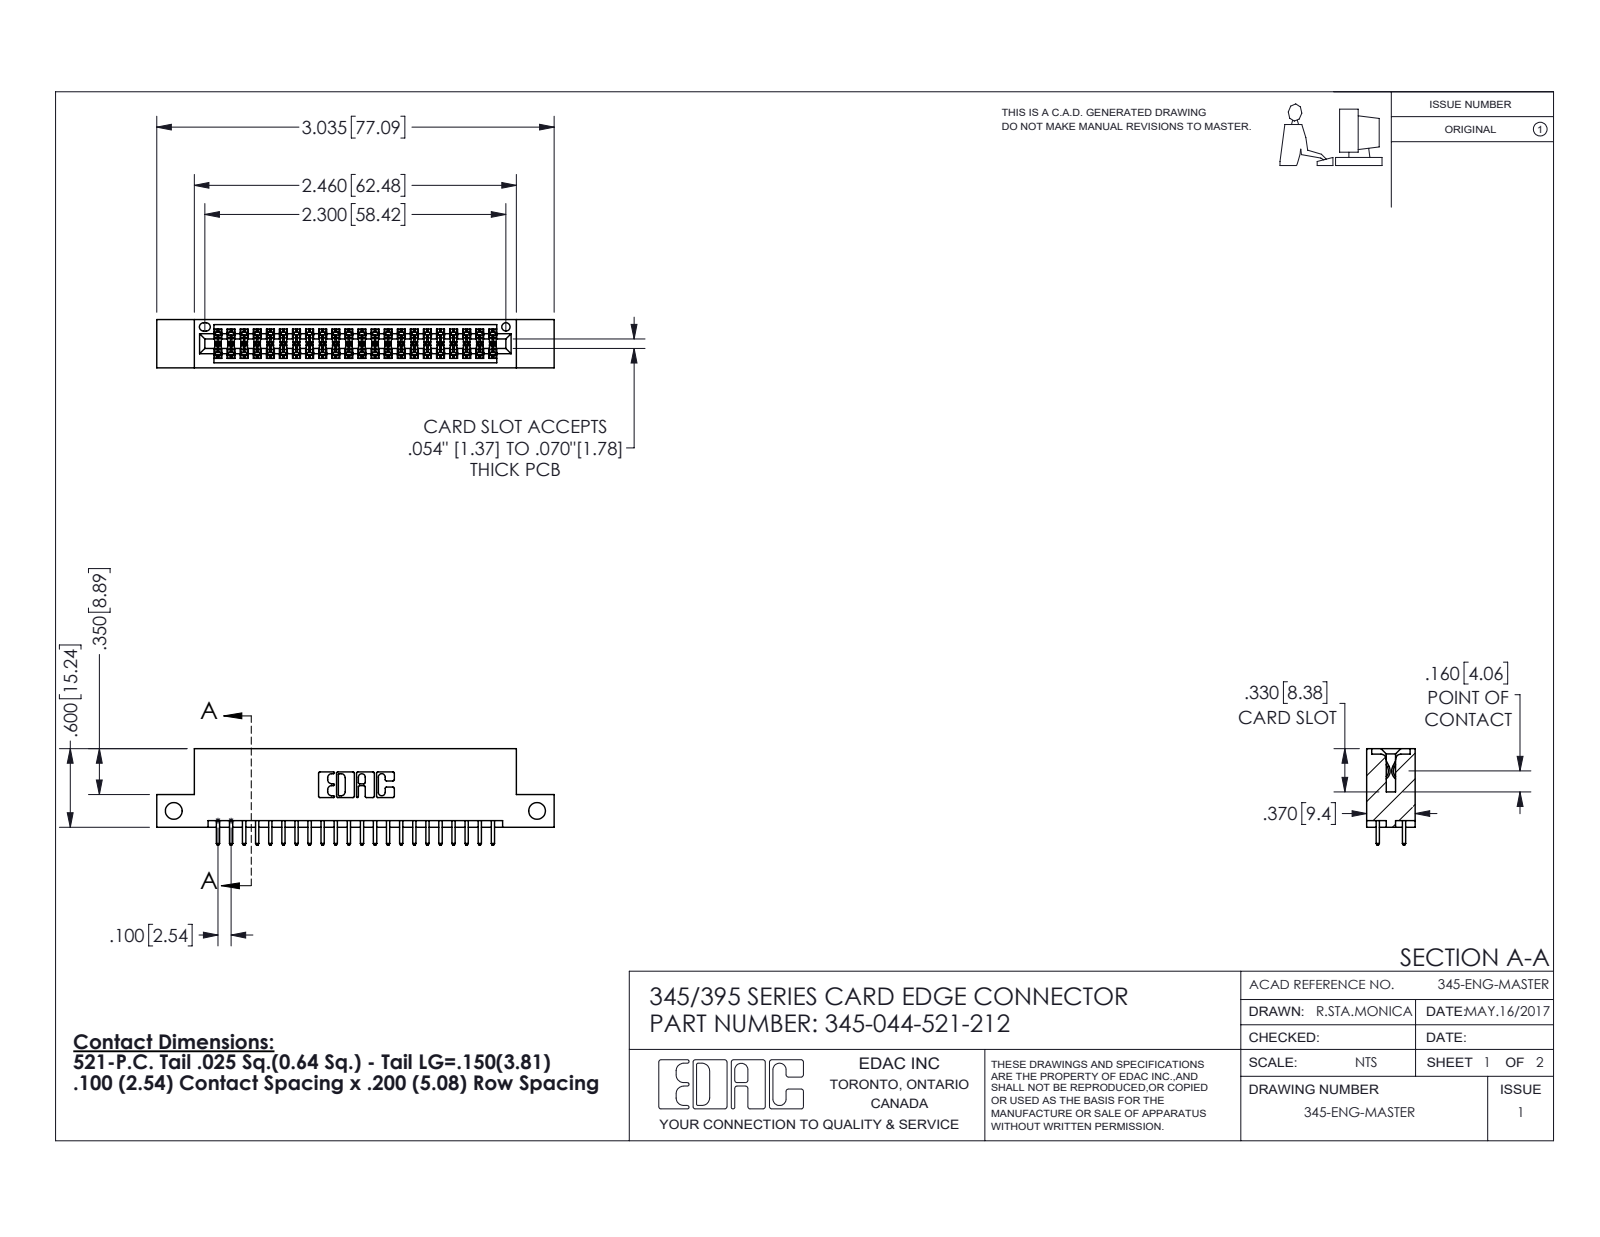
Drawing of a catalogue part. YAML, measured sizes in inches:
part_name: "345-044-521-212; 345 Part_Flush Mounting Lugs - Side Mount; 345-292-001_345-293-121"
step_written_by: "SolidWorks 2016 (CONFIG_CONTROL_DESIGN)"
units: inches
bodies: {solids: 45, faces: 2326, planar: 1532, cylindrical: 794, other: 0}
overall_size: [3.035, 0.737, 0.37]
volume: 0.439
surface_area: 15.5
round_holes:
  - {diameter: 0.128, count: 2}
  - {diameter: 0.064, count: 1}
partial_cylinders:
  - {radius: 0.006, count: 66}
  - {radius: 0.01, count: 44}
  - {radius: 0.01, count: 22}
  - {radius: 0.007, count: 6}
  - {radius: 0.031, count: 6}
  - {radius: 0.026, count: 3}
  - {radius: 0.014, count: 2}
  - {radius: 0.019, count: 2}
face_to_face_distances: [0.298, 0.072, 0.2, 0.37, 0.098, 0.272, 0.025, 0.225, 0.175, 0.149]
hole_center_spacings: [2.775]
